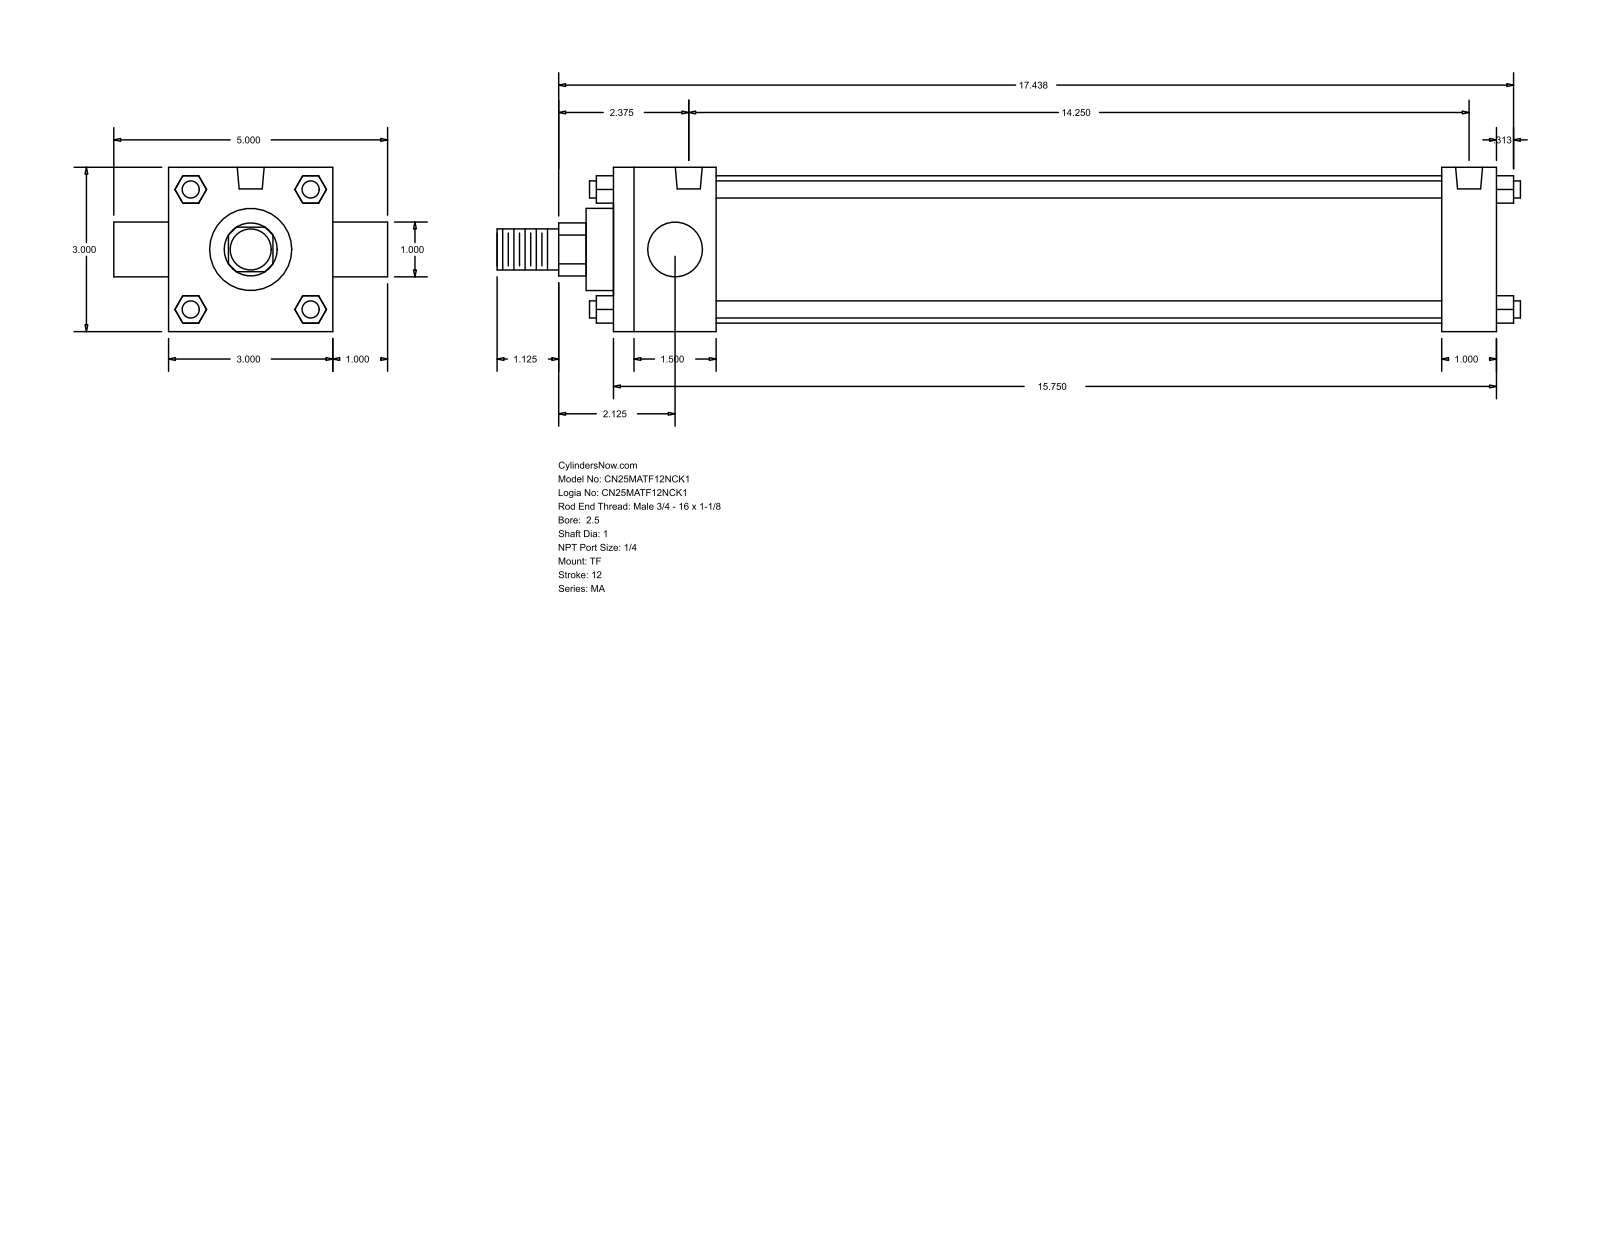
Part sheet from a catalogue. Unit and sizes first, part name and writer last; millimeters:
Units: millimetres
Overall size (bounding box): 474.66 × 127 × 76.2
Round holes (diameter × count): ⌀7.94 ×3, ⌀12.49 ×2
Round bosses / shafts (diameter × count): ⌀7.94 ×4, ⌀25.4 ×2, ⌀68.33 ×1, ⌀38.1 ×1, ⌀19.05 ×1
Partial cylindrical surfaces — rounded edges, fillets, slot ends (radius × count): R12.29 ×1
Main face-to-face distances: 76.2, 409.58, 12.7, 47.63, 384.17, 336.54, 361.95, 25.41, 101.6, 25.4
Hole centre spacings: 361.94
Bodies: 0 solids, 120 faces (92 planar, 28 cylindrical, 0 other)
Part name (STEP PRODUCT): MA_TF__0250_1
STEP written by: GSSL Pune (CONFIG_CONTROL_DESIGN)
